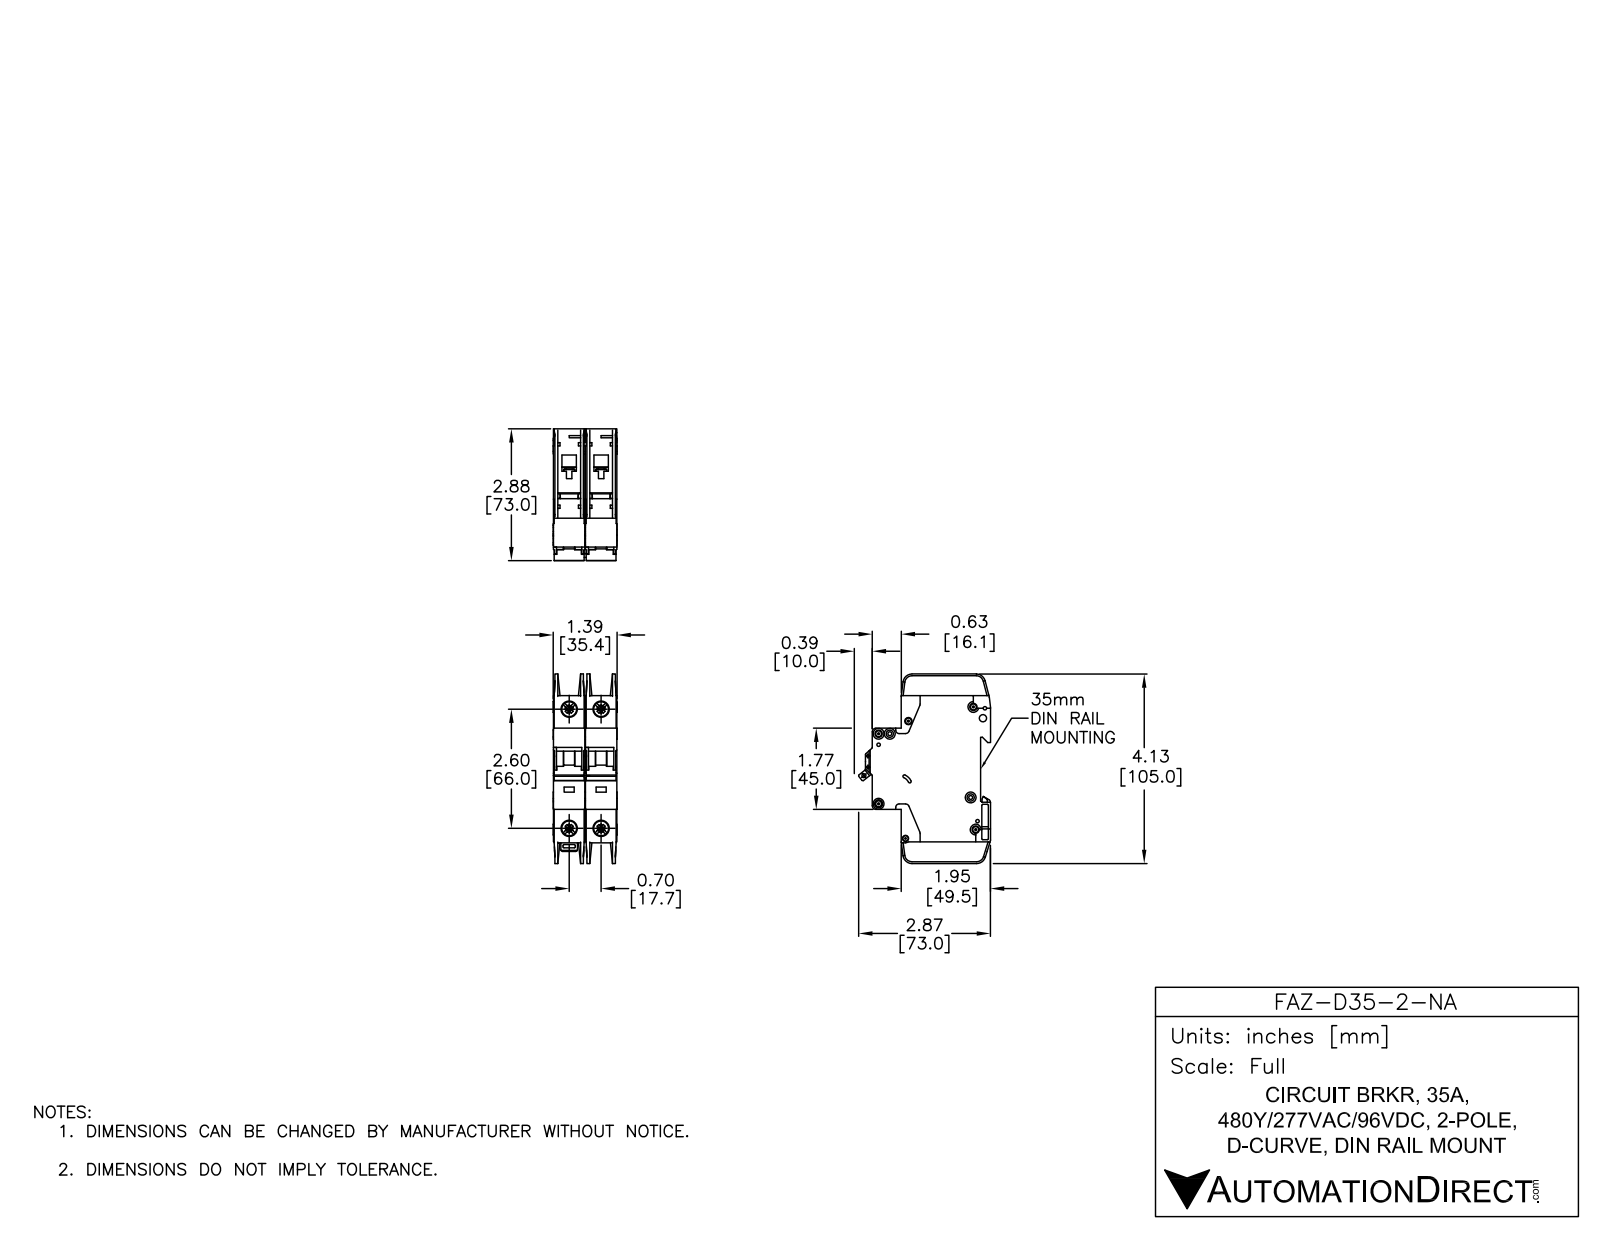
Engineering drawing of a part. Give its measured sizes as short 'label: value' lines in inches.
name: FAZ-D35-2-NA
written by: SolidWorks 2014 (AUTOMOTIVE_DESIGN)
unit: in
bodies: 6 solids, 1568 faces (818 planar, 526 cylindrical, 224 other)
size: 4.134 × 2.876 × 1.394
volume: 9.482 in³; area: 76.69 in²
holes: 7× ⌀0.142, 4× ⌀0.281, 4× ⌀0.323, 2× ⌀0.043, 2× ⌀0.059, 2× ⌀0.157, 1× ⌀0.075, 1× ⌀0.085, 1× ⌀0.087, 1× ⌀0.1, 1× ⌀0.13, 1× ⌀0.134
bosses: 7× ⌀0.236, 2× ⌀0.098
rounds: 47× R0.01, 24× R0.02, 18× R0.039, 12× R0.079, 5× R0.197, 4× R0.071, 4× R0.157, 2× R0.008
face distances: 0.697, 0.689, 0.028, 0.593, 0.096, 0.069, 0.62, 0.524, 1.386, 0.669
hole spacings: 0.244, 0.697, 2.598, 2.69, 0.204, 0.24, 0.322, 0.337
